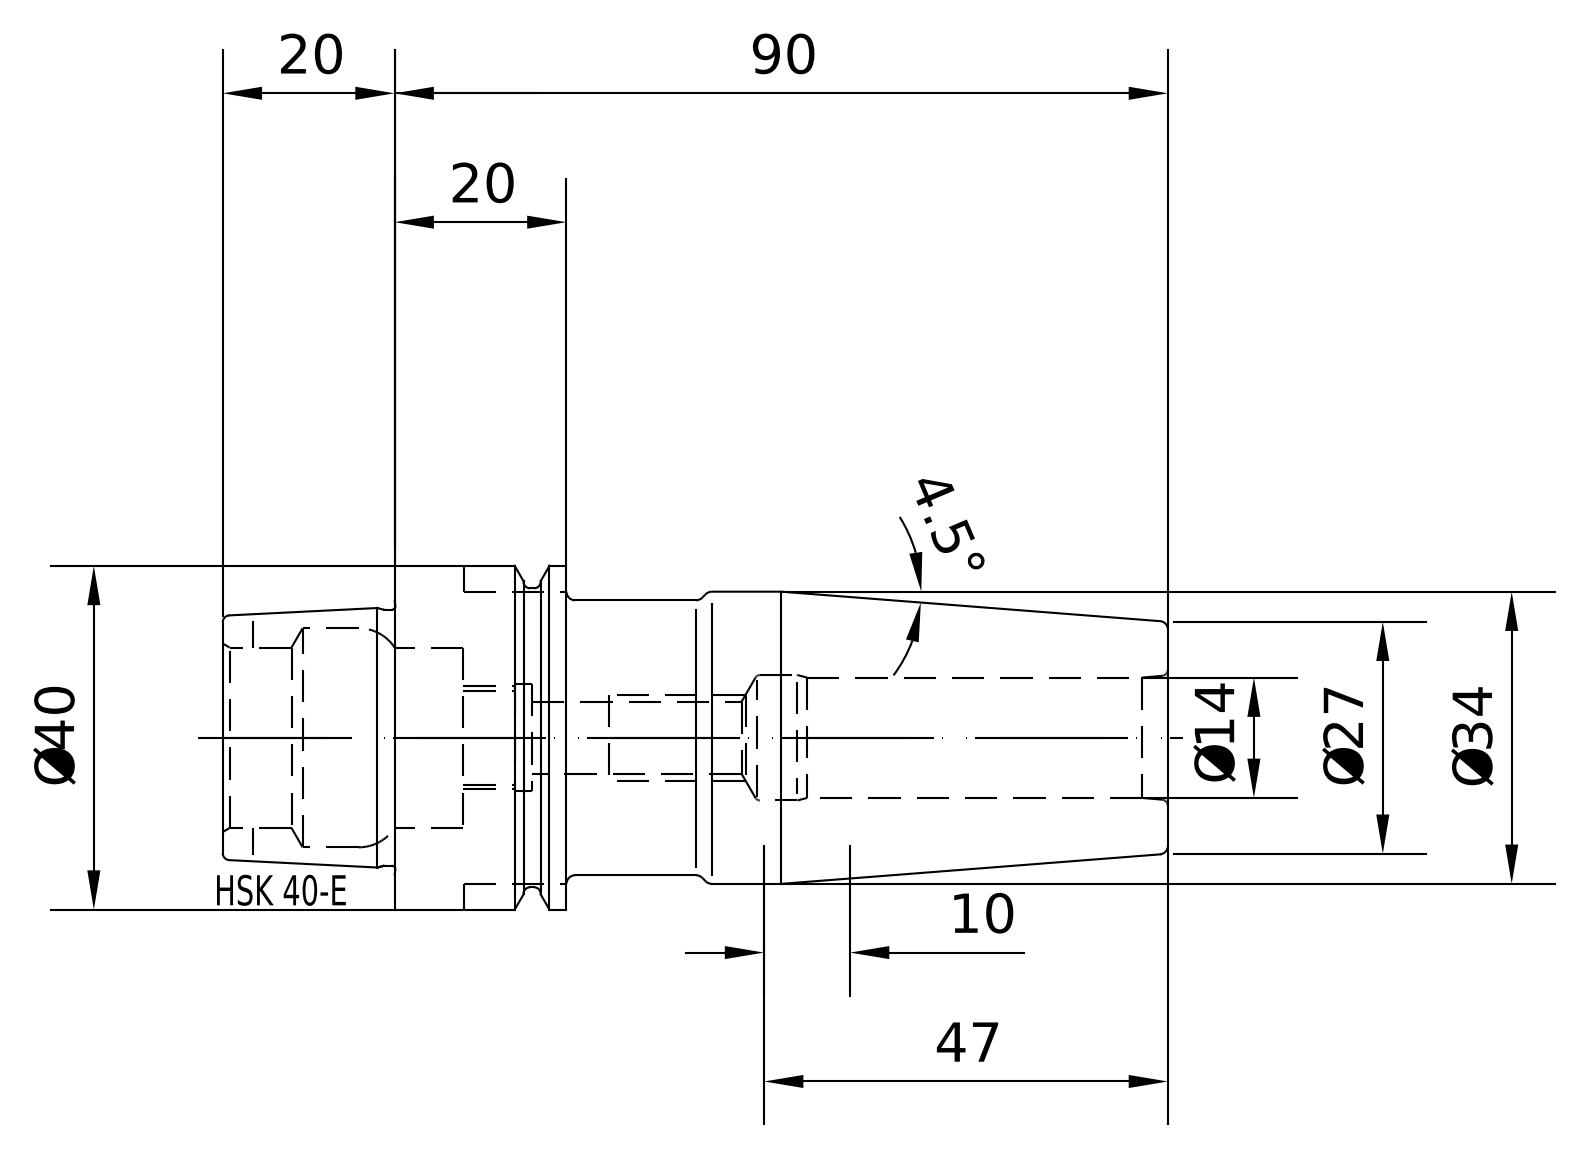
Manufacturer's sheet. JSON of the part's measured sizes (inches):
{"part_name": "E40-140-14", "step_written_by": "PRO/ENGINEER BY PARAMETRIC TECHNOLOGY CORPORATION, 2010430 (CONFIG_CONTROL_DESIGN)", "units": "inches", "bodies": {"solids": 1, "faces": 87, "planar": 9, "cylindrical": 26, "other": 52}, "overall_size": [4.327, 1.575, 1.575], "volume_in3": 4.42, "surface_area_in2": 28.33, "round_holes": [[0.402, 1], [0.481, 1], [0.492, 1], [0.551, 1], [0.828, 1], [1.007, 1]], "round_bosses_or_shafts": [[1.575, 1], [1.368, 1], [1.339, 1], [1.26, 1], [1.174, 1]], "face_to_face_distances": [0.785, 3.543, 2.758, 0.783, 1.569, 4.327, 1.096, 0.313, 0.472, 3.23]}
